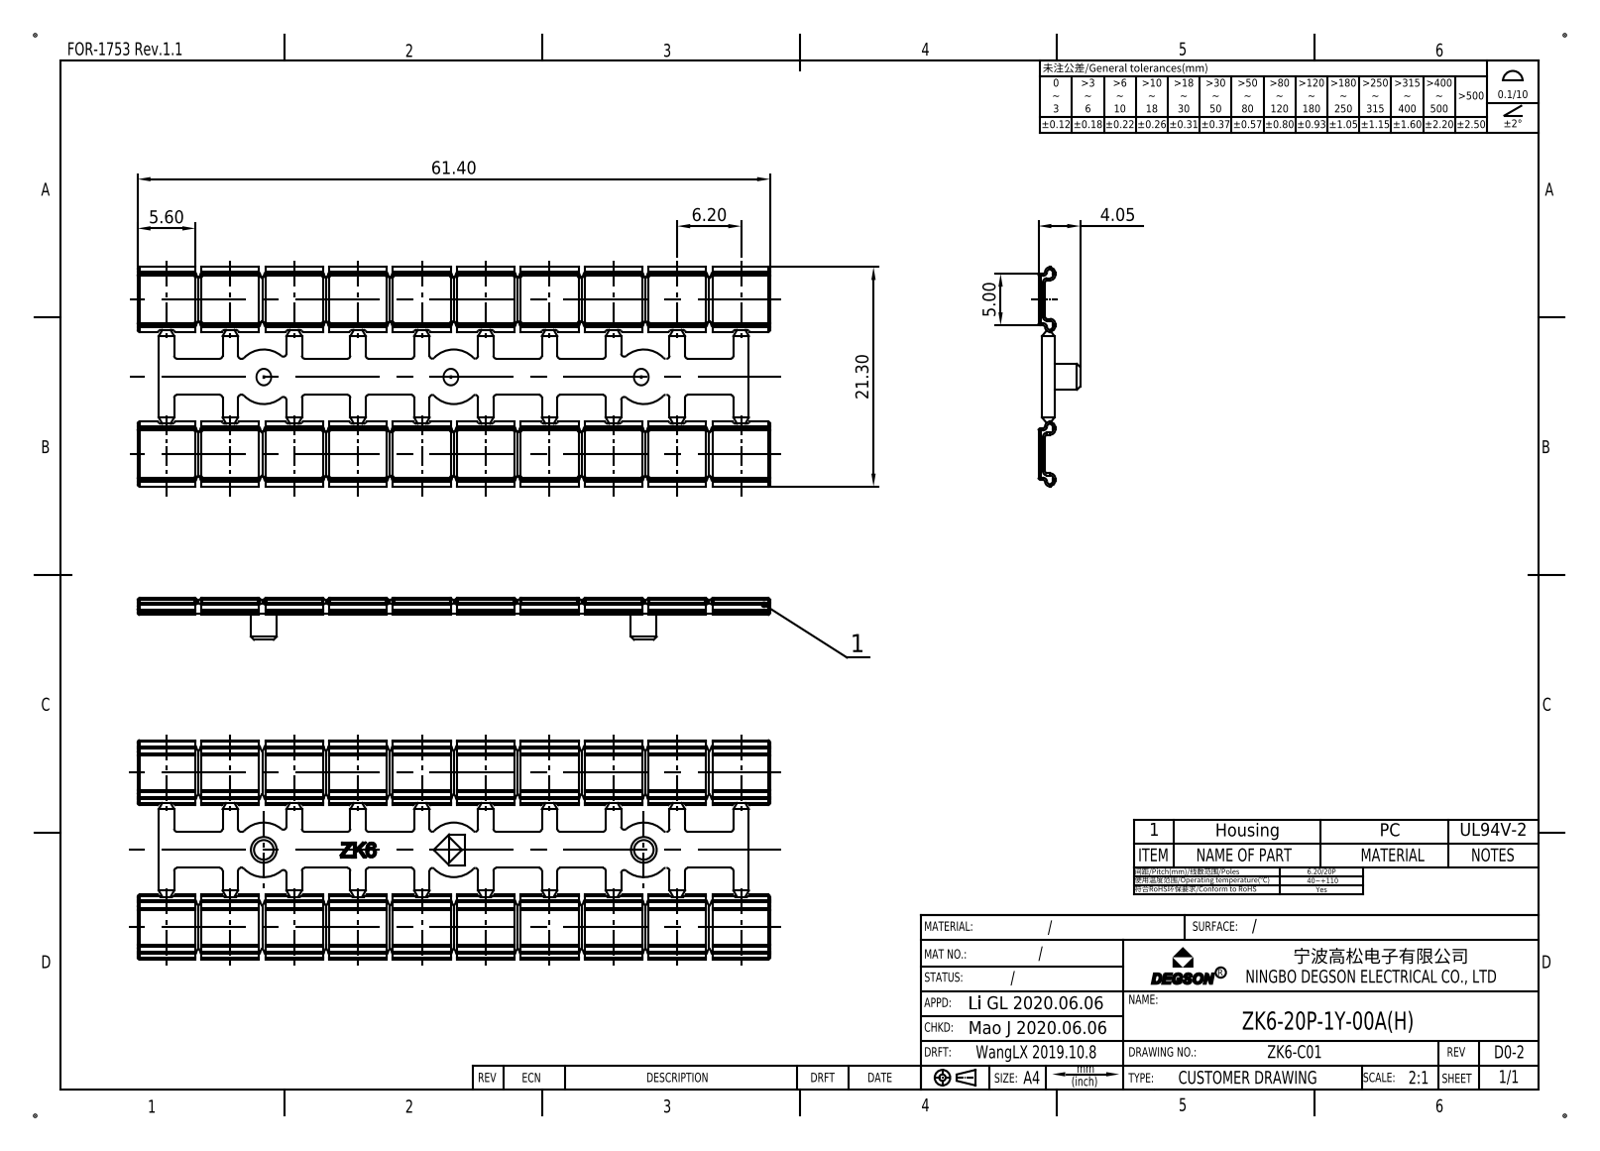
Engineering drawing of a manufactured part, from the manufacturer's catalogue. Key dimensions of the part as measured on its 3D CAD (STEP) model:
Part name (STEP PRODUCT): ZK6-20P-19-01AH-D0-1
STEP written by: SolidWorks 2012 (CONFIG_CONTROL_DESIGN)
Units: millimetres
Bodies: 1 solid, 1479 faces (736 planar, 531 cylindrical, 212 other)
Overall size (bounding box): 61.4 × 21.3 × 4.05
Volume: 995 mm³ · Surface area: 2 887 mm²
Round bosses / shafts (diameter × count): ⌀2.5 ×2
Partial cylindrical surfaces — rounded edges, fillets, slot ends (radius × count): R0.2 ×194, R0.3 ×84, R0.5 ×12, R2.65 ×3
Main face-to-face distances: 0.64, 0.35, 1.55, 0.91, 1.2, 6.2, 15, 12.4, 18.6, 3.97
